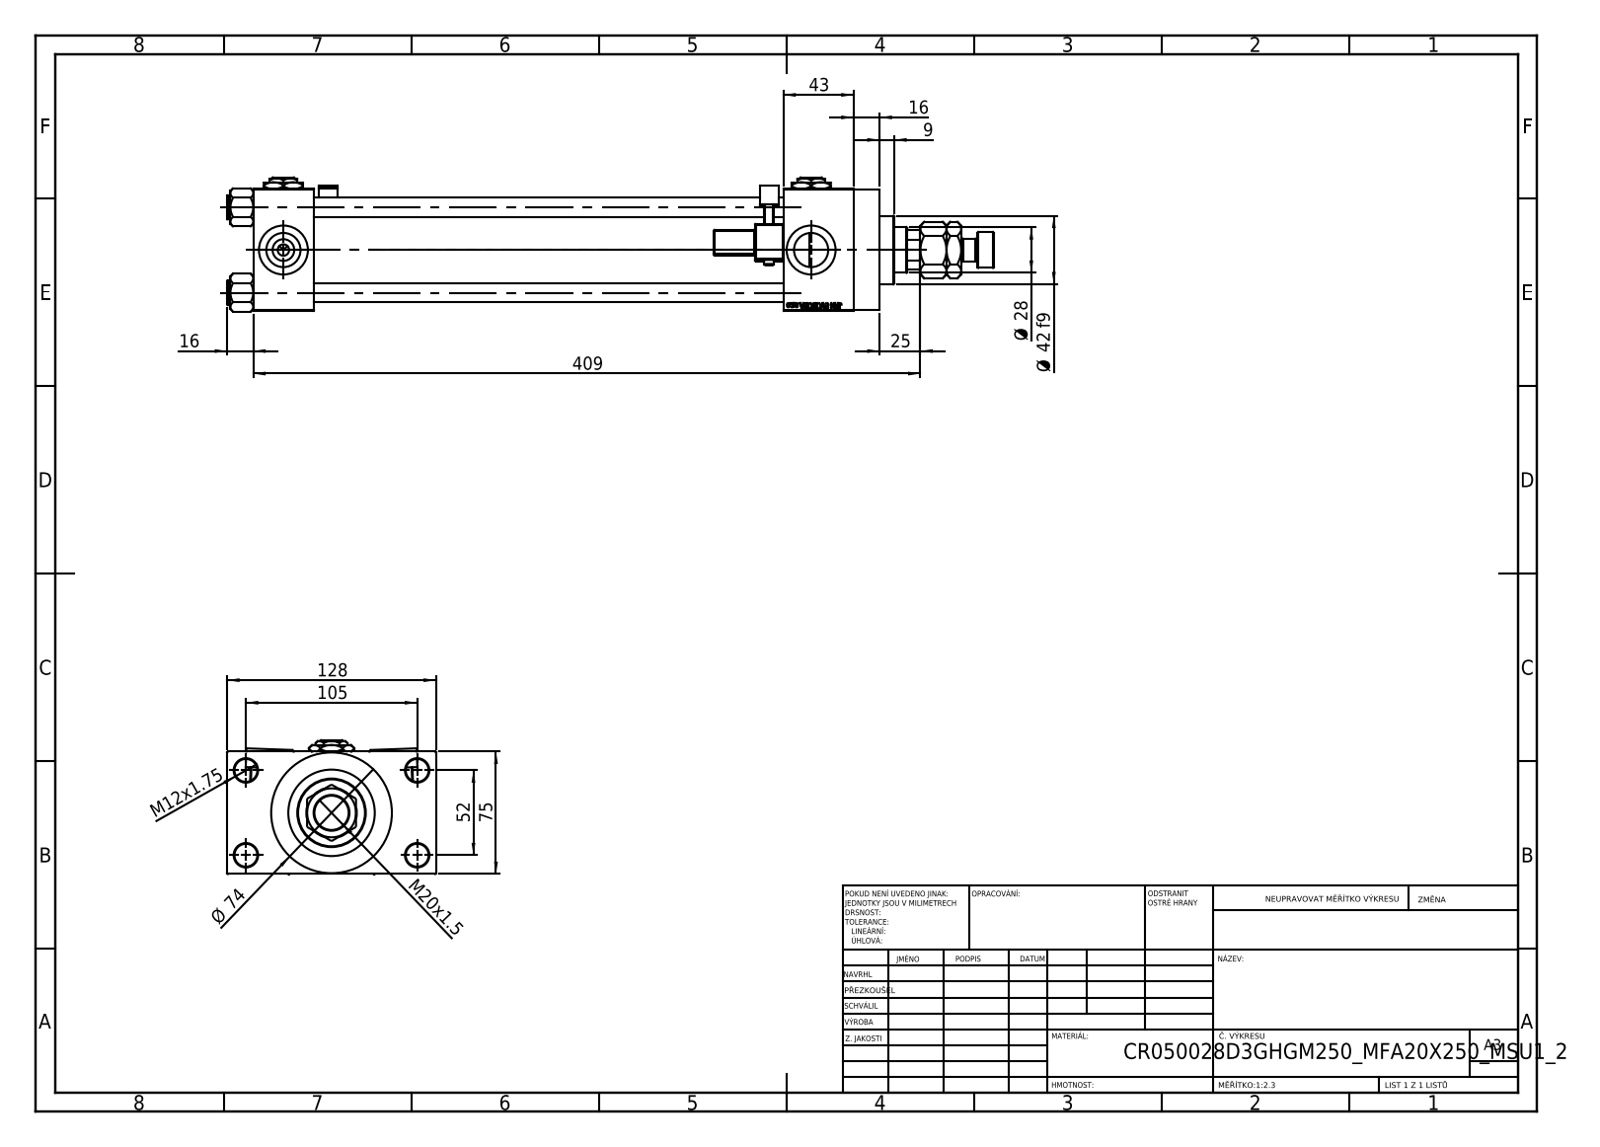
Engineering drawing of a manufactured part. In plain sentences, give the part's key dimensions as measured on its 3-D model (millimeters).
The part is named "V215CR_MSU; MFA; Zatka_pro_OIL_PORT; V215CR_D_Body (+4 more)". Its 3-D file was written by "SolidWorks 2019 (CONFIG_CONTROL_DESIGN)". It is 16 solids with 1410 faces: 619 planar, 163 cylindrical and 628 other. Overall it measures 470 by 128 by 82.27 millimeters. Its volume is 1 228 000 cubic millimeters and its surface area 324 208 square millimeters. Round holes: 4 of diameter 12, 4 of diameter 14, 4 of diameter 20.96, 4 of diameter 30, 3 of diameter 7, 1 of diameter 18.5, 1 of diameter 28, 1 of diameter 31, 1 of diameter 41, 1 of diameter 50, 1 of diameter 53. Round bosses or shafts: 4 of diameter 15, 2 of diameter 6, 1 of diameter 74, 1 of diameter 56, 1 of diameter 42, 1 of diameter 22, 1 of diameter 14. Partial cylindrical surfaces (rounded edges, fillets, slot ends): 48 of radius 0.5, 2 of radius 1, 2 of radius 2.5, 2 of radius 4, 1 of radius 13.5. The main face-to-face distances are 75, 288, 37, 325, 26.5, 101.5, 368, 331, 43, 16. The hole center spacings are 26.35, 36.98, 52.3, 58.43, 58.59, 78.65, 94.37, 52.
